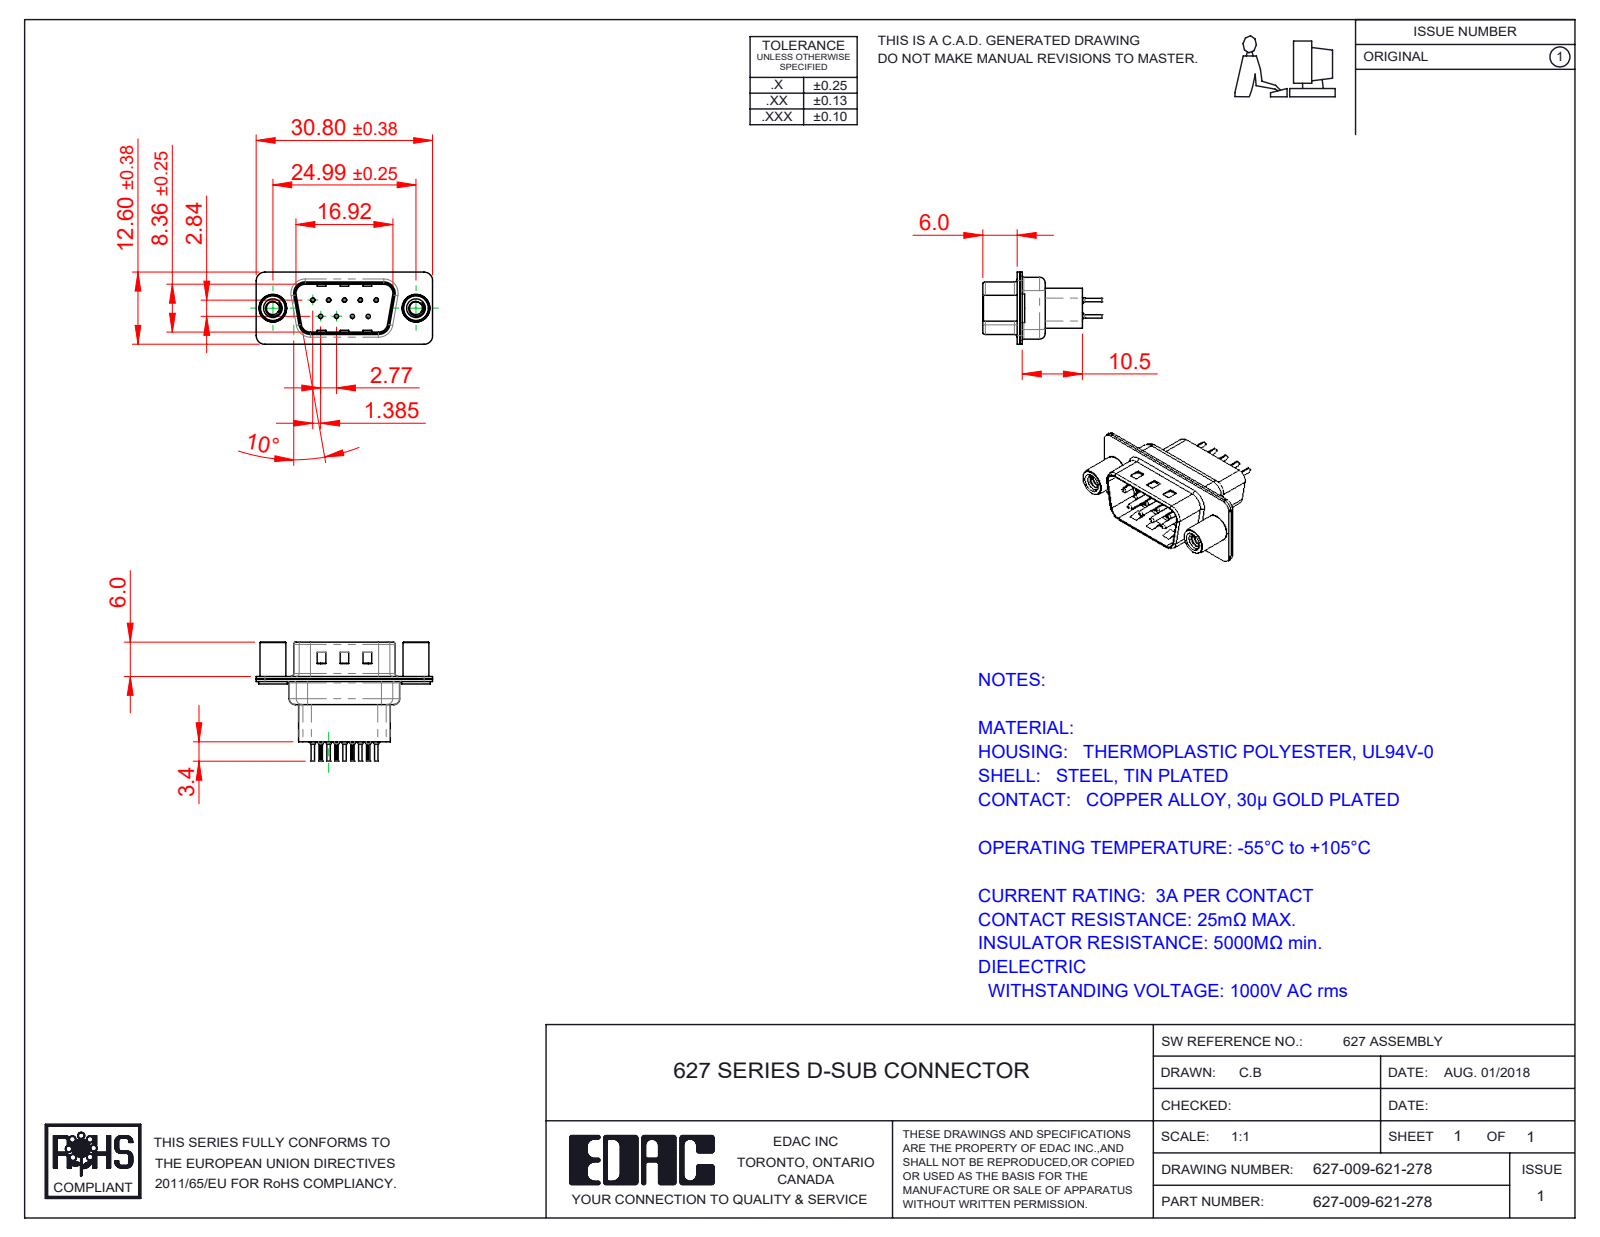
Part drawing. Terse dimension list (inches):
name: 627 4-40 Threaded Standoff; 627 Contact Row 2_21H; 627 Shell Rear_09 Contacts; 627 Shell Front_09 Contacts (+3 more)
written by: SolidWorks 2020 (CONFIG_CONTROL_DESIGN)
unit: in
bodies: 14 solids, 1220 faces (325 planar, 490 cylindrical, 405 other)
size: 1.213 × 0.819 × 0.496
volume: 0.112 in³; area: 7.586 in²
holes: 9× ⌀0.008, 9× ⌀0.014, 9× ⌀0.043, 9× ⌀0.063, 2× ⌀0.089, 2× ⌀0.157, 2× ⌀0.189
bosses: 9× ⌀0.079, 9× ⌀0.059, 9× ⌀0.03, 9× ⌀0.024, 2× ⌀0.197, 2× ⌀0.193, 2× ⌀0.177
rounds: 18× R0.004, 18× R0.059, 12× R0.079, 8× R0.02, 8× R0.063, 4× R0.01, 4× R0.024, 4× R0.026
face distances: 0.016, 0.018, 0.035, 0.032, 0.377, 0.055, 0.059, 0.027, 0.302, 0.043
hole spacings: 0.124, 0.109, 0.218, 0.198, 0.198, 0.327, 0.294, 0.295
